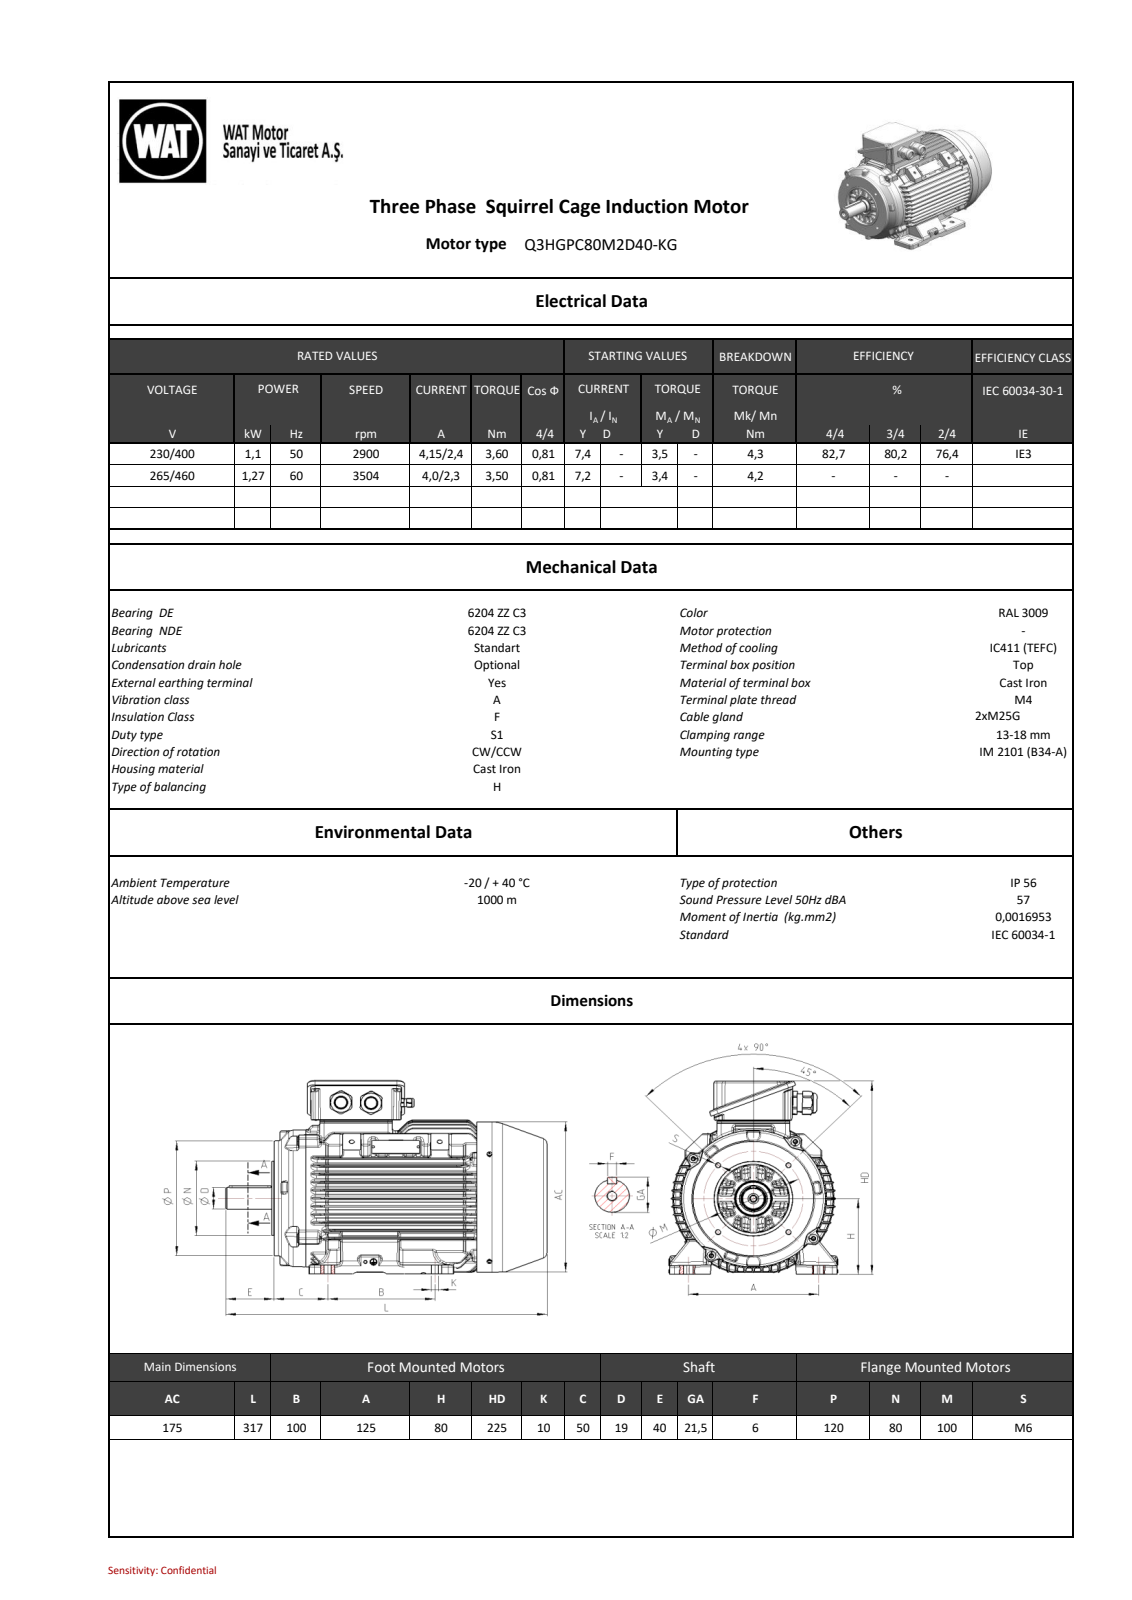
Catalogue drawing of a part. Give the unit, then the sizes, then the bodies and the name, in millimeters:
Units: millimetres
Overall size (bounding box): 316.71 × 224.98 × 221.33
Round holes (diameter × count): ⌀5 ×4, ⌀10 ×3, ⌀2.5 ×2, ⌀3.3 ×2, ⌀17.2 ×2, ⌀6.4 ×1, ⌀6.5 ×1, ⌀27.8 ×1, ⌀28 ×1, ⌀168 ×1
Round bosses / shafts (diameter × count): ⌀20 ×4, ⌀9.2 ×3, ⌀8.65 ×3, ⌀8.5 ×3, ⌀8 ×3, ⌀5 ×3, ⌀27.7 ×2, ⌀25.25 ×2
Partial cylindrical surfaces — rounded edges, fillets, slot ends (radius × count): R1.5 ×278, R2.5 ×46, R1.8 ×38, R1 ×34, R2 ×24, R4 ×24, R5 ×22, R0.2 ×15
Main face-to-face distances: 41.78, 62.56, 276.71, 234.93, 3.01, 1.5, 3, 152.95, 215.51, 1.53
Hole centre spacings: 70.71, 50, 100, 40, 49.99, 50.01, 74.99, 77.95
Bodies: 0 solids, 2811 faces (766 planar, 786 cylindrical, 1259 other)
Part name (STEP PRODUCT): 26000A30F4D8roov
STEP written by: SIEMENS PLM Software NX 11.0 (AUTOMOTIVE_DESIGN)
